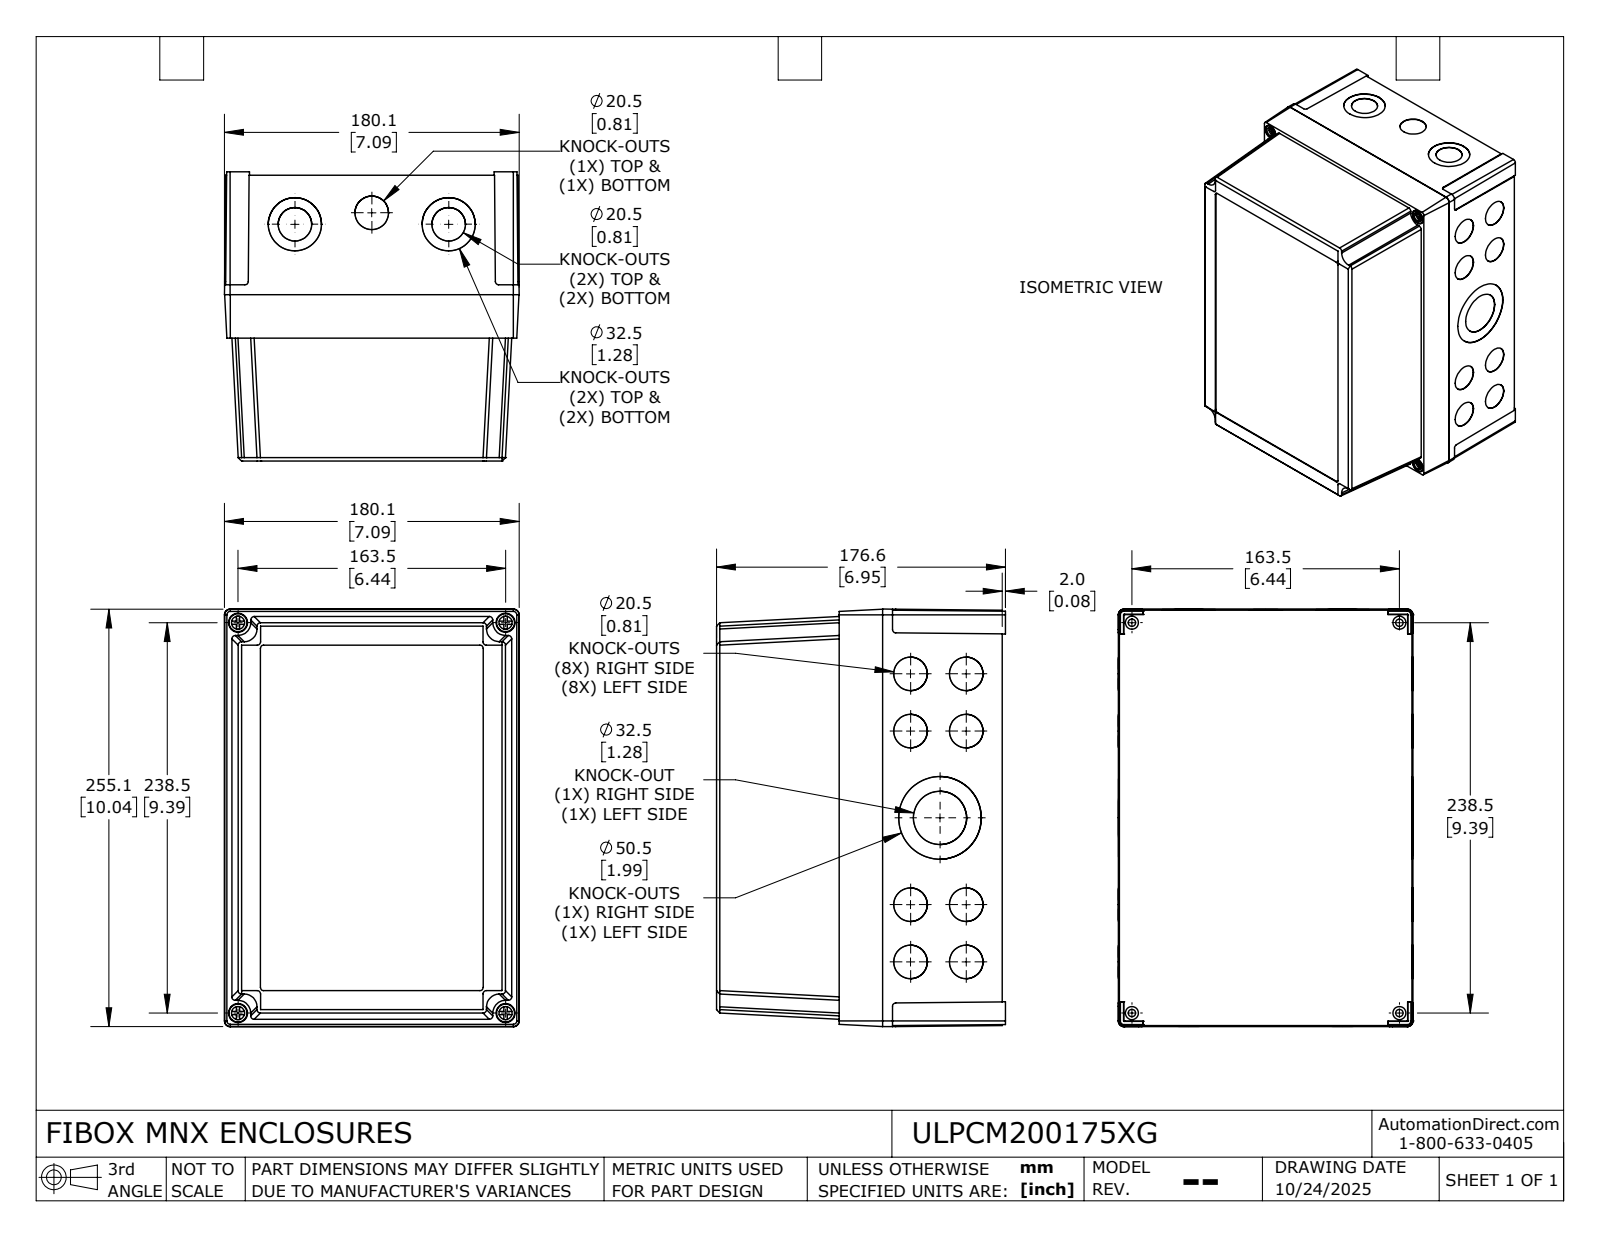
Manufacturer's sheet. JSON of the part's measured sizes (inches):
{"part_name": "ULPCM200175XG_Default", "step_written_by": "SolidWorks 2024 (CONFIG_CONTROL_DESIGN)", "units": "inches", "bodies": {"solids": 6, "faces": 791, "planar": 437, "cylindrical": 308, "other": 46}, "overall_size": [10.043, 7.091, 6.953], "volume_in3": 41.59, "surface_area_in2": 745.5, "round_holes": [[0.807, 22], [0.126, 20], [0.157, 20], [1.28, 6], [0.177, 4], [0.315, 4], [0.457, 4], [1.988, 2]], "round_bosses_or_shafts": [[0.315, 16], [0.098, 8], [0.433, 4], [0.283, 4], [0.276, 4]], "partial_cylinders_radius": [[0.079, 8], [0.083, 8], [0.112, 6], [0.042, 4], [0.197, 4], [0.307, 4], [0.046, 2]], "face_to_face_distances": [0.059, 0.118, 6.756, 0.165, 6.638, 0.098, 6.854, 6.736, 0.18, 0.12], "hole_center_spacings": [1.378, 1.339, 1.921, 1.939, 5.046, 5.551, 5.71, 4.921]}
